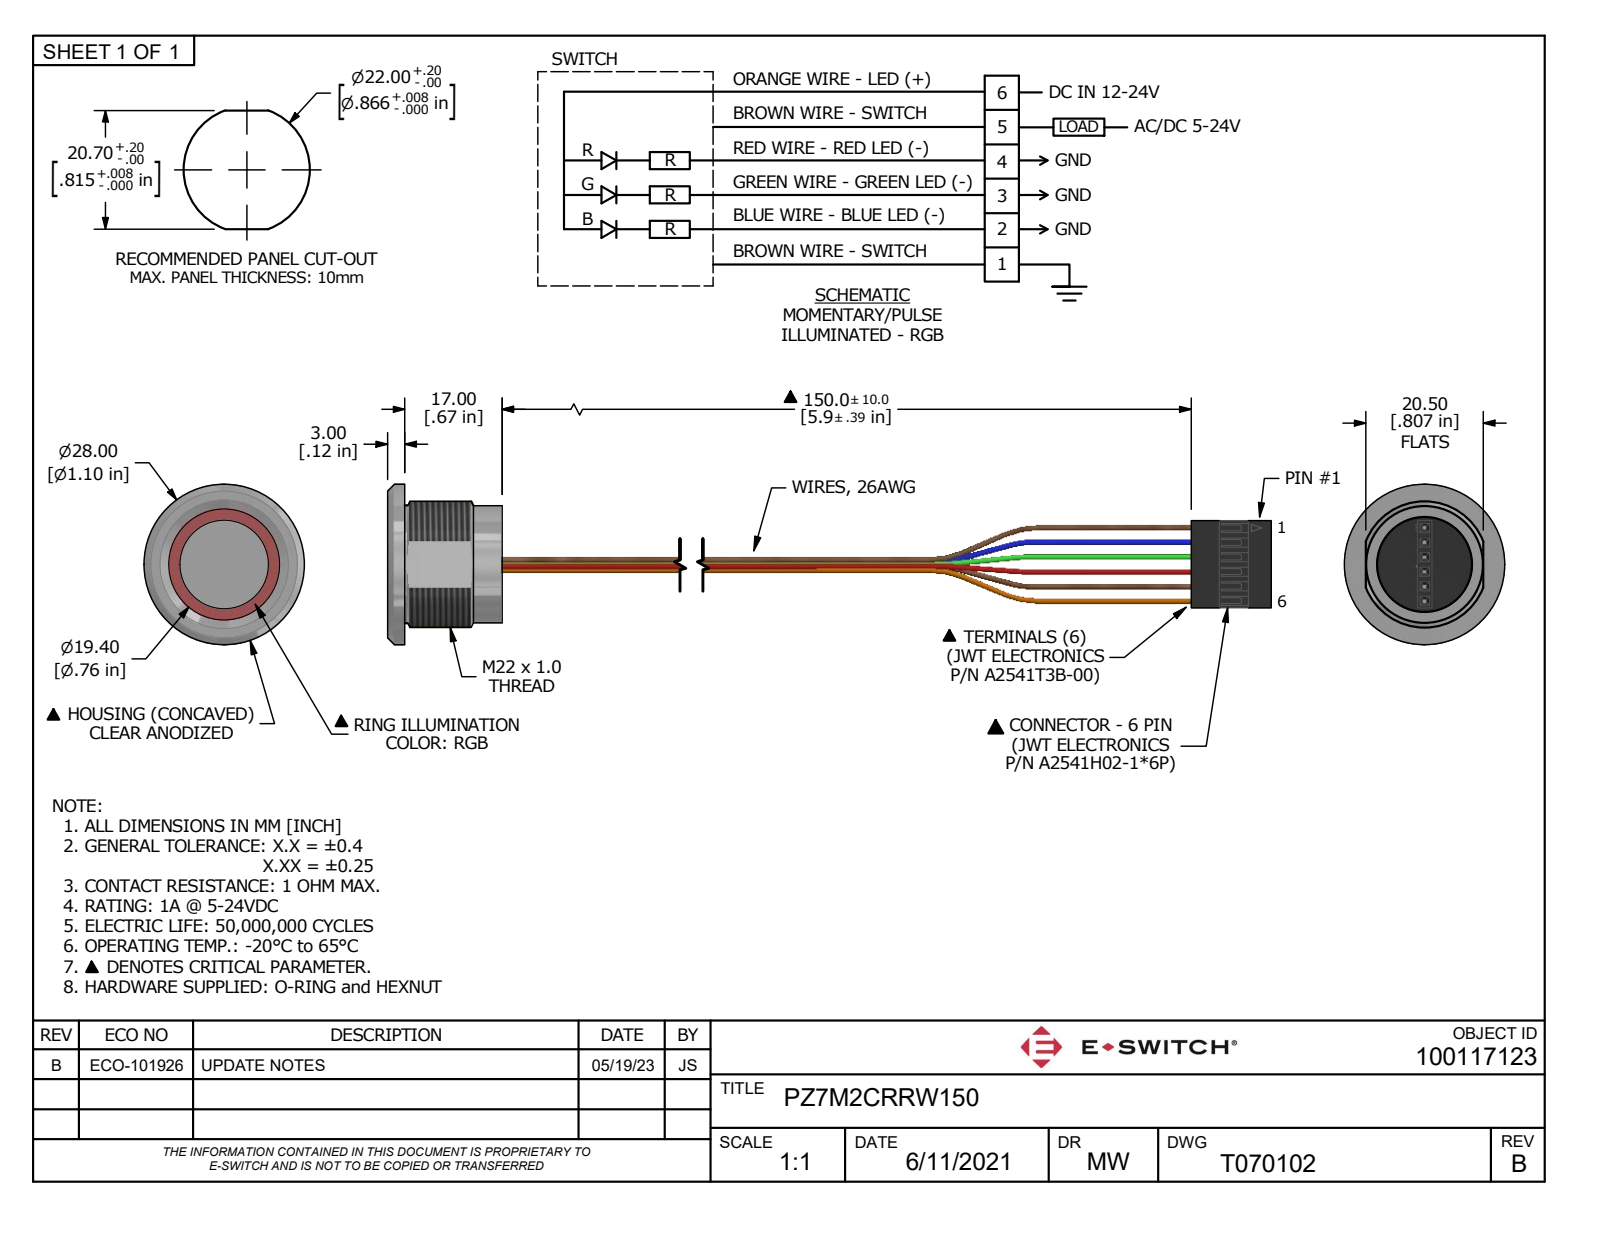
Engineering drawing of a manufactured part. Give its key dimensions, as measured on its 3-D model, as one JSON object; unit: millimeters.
{"part_name": "PZ7M2CRRW150", "step_written_by": "Autodesk Inventor 2020 (AUTOMOTIVE_DESIGN)", "units": "millimeters", "bodies": {"solids": 5, "faces": 208, "planar": 141, "cylindrical": 42, "other": 25}, "overall_size": [184, 28, 28], "volume_mm3": 8558, "surface_area_mm2": 6550, "round_holes": [[19.4, 1]], "round_bosses_or_shafts": [[1, 16], [0.7, 6], [28, 1], [20.6, 1], [20.4, 1], [15.4, 1]], "partial_cylinders_radius": [[0.25, 12], [11, 1]], "face_to_face_distances": [2.54, 0.47, 2.07, 2, 8.98, 11.52, 1.6, 11.05, 9.45, 5.08]}
